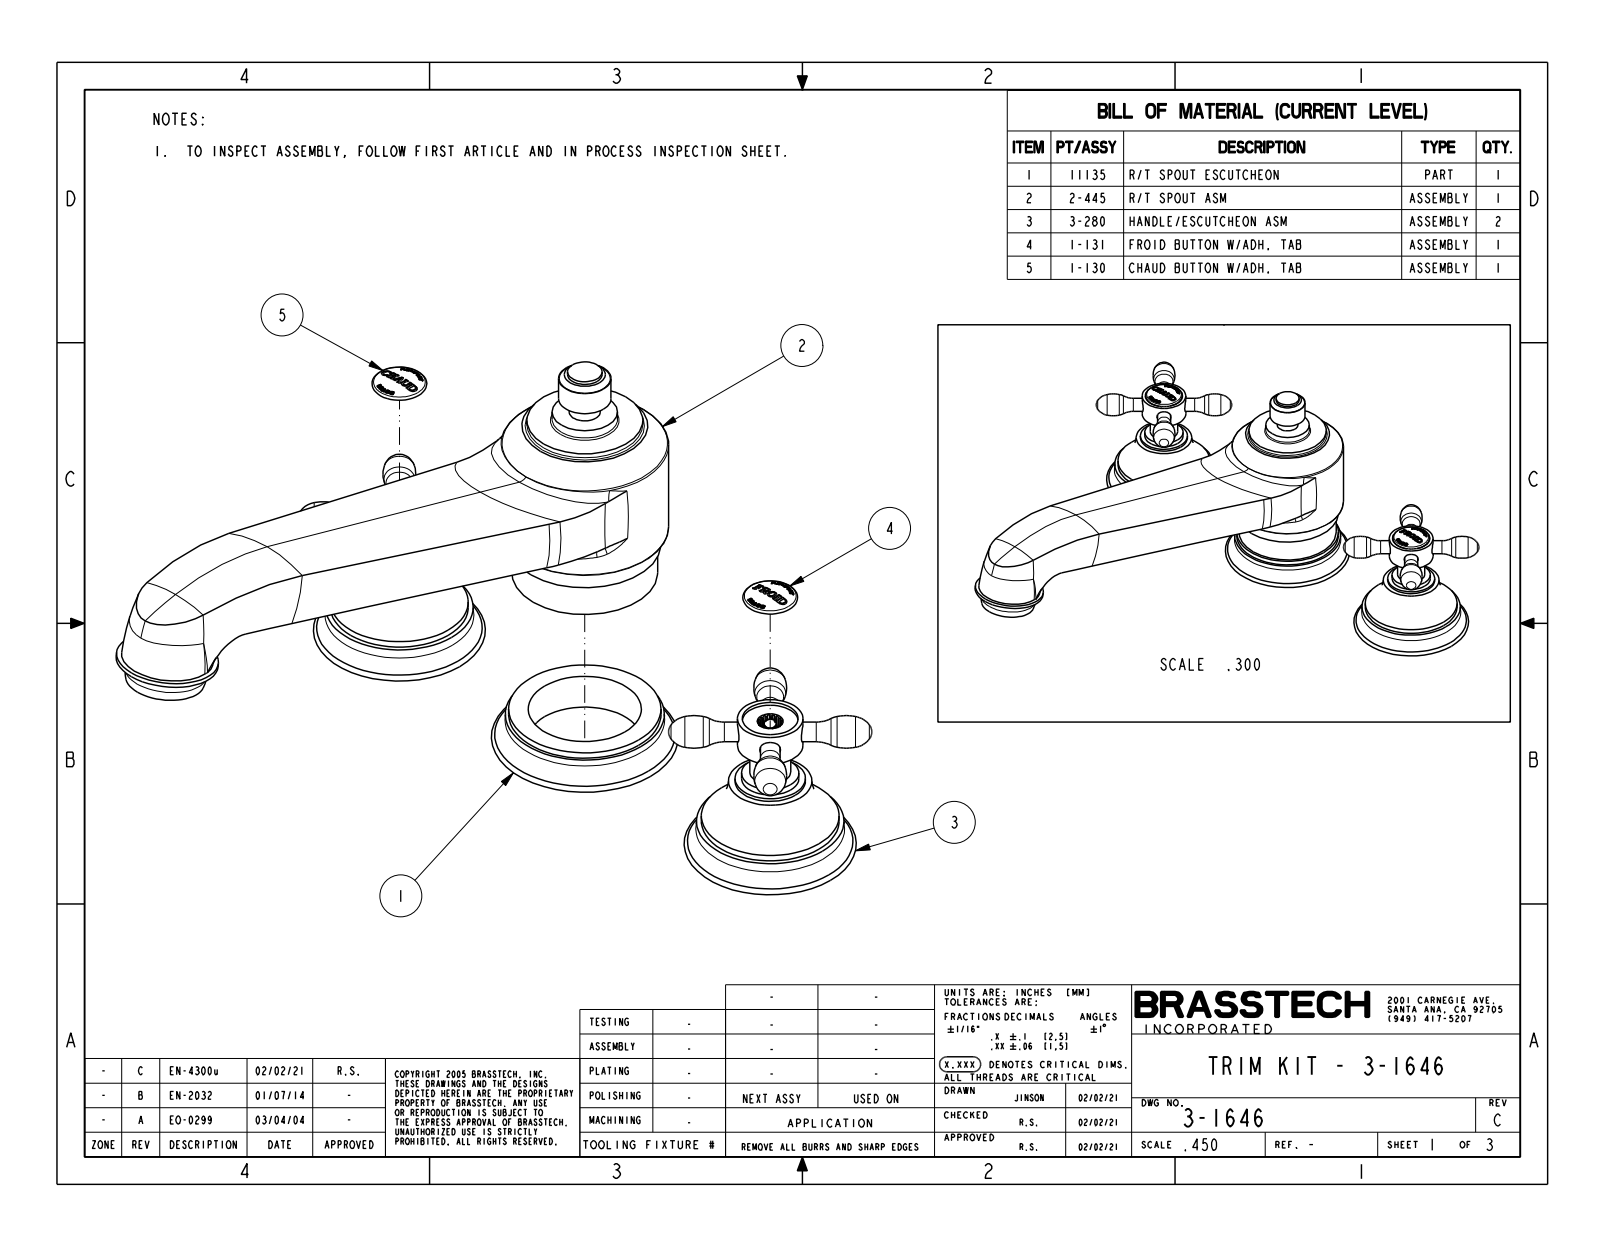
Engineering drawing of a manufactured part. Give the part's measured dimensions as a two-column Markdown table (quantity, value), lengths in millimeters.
| quantity | value |
| --- | --- |
| part name | 3-1646 |
| STEP written by | CREO PARAMETRIC BY PTC INC, 2018400 (CONFIG_CONTROL_DESIGN) |
| units | millimeters |
| bodies | 3 solids, 993 faces (412 planar, 324 cylindrical, 257 other) |
| overall size | 284.8 × 269.9 × 118 |
| volume | 689 100 mm³ |
| surface area | 89 480 mm² |
| round holes (diameter × count) | 8 × 4, 21.6 × 2 |
| round bosses / shafts (diameter × count) | 7.6 × 8, 25.4 × 3, 53.3 × 2, 27.3 × 2, 22.2 × 2, 15.9 × 2, 10.2 × 2, 65 × 1 |
| partial cylindrical surfaces (radius × count) | 0.3 × 28, 0.6 × 17, 0.2 × 14, 0.4 × 14, 0.1 × 10, 0.4 × 9, 0.2 × 8, 0.3 × 8 |
| main face-to-face distances | 86.9, 12.1, 74.8, 22.9, 2.5, 20.3, 34.9, 51.9, 31.1, 19.1 |
| hole center spacings | 143.7, 203.2 |
